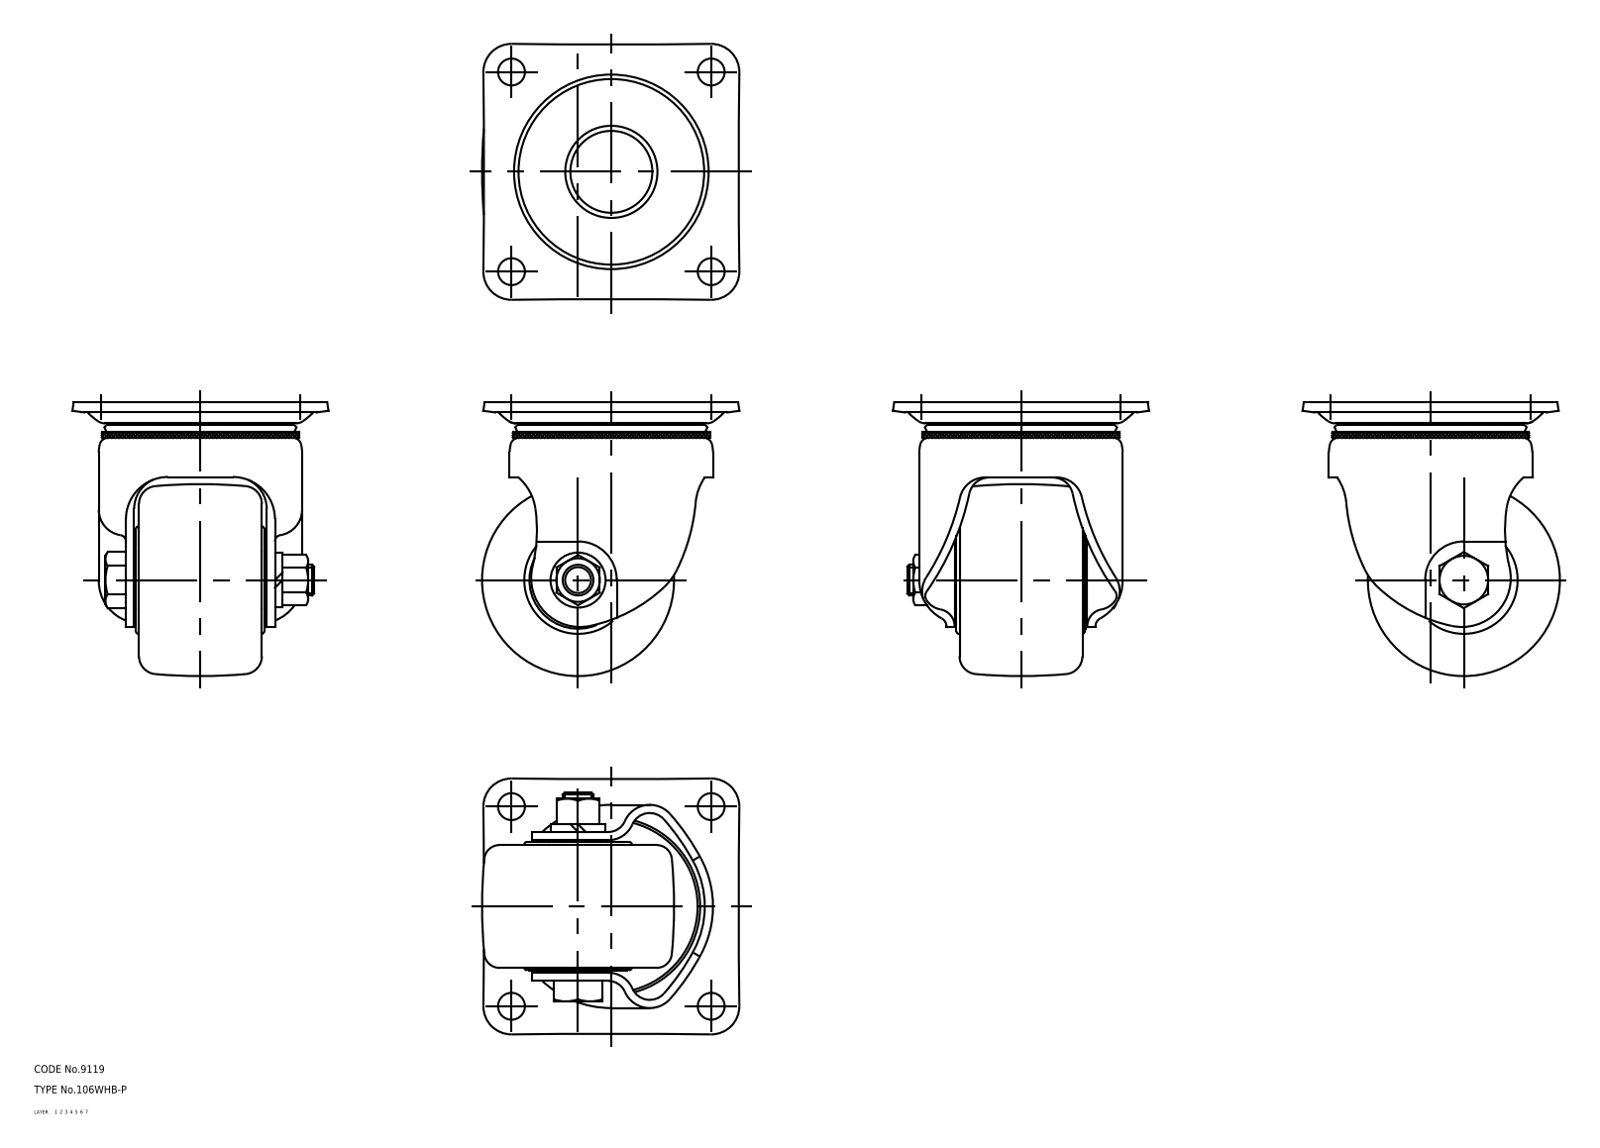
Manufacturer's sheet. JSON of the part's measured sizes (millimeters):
{"part_name": "67129849; 67129862; 67129875; 67129888 (+1 more)", "step_written_by": "CADfix (AUTOMOTIVE_DESIGN)", "units": "millimeters", "bodies": {"solids": 5, "faces": 276, "planar": 0, "cylindrical": 0, "other": 276}, "overall_size": [107, 100.5, 100], "volume_mm3": 366678, "surface_area_mm2": 85101}
